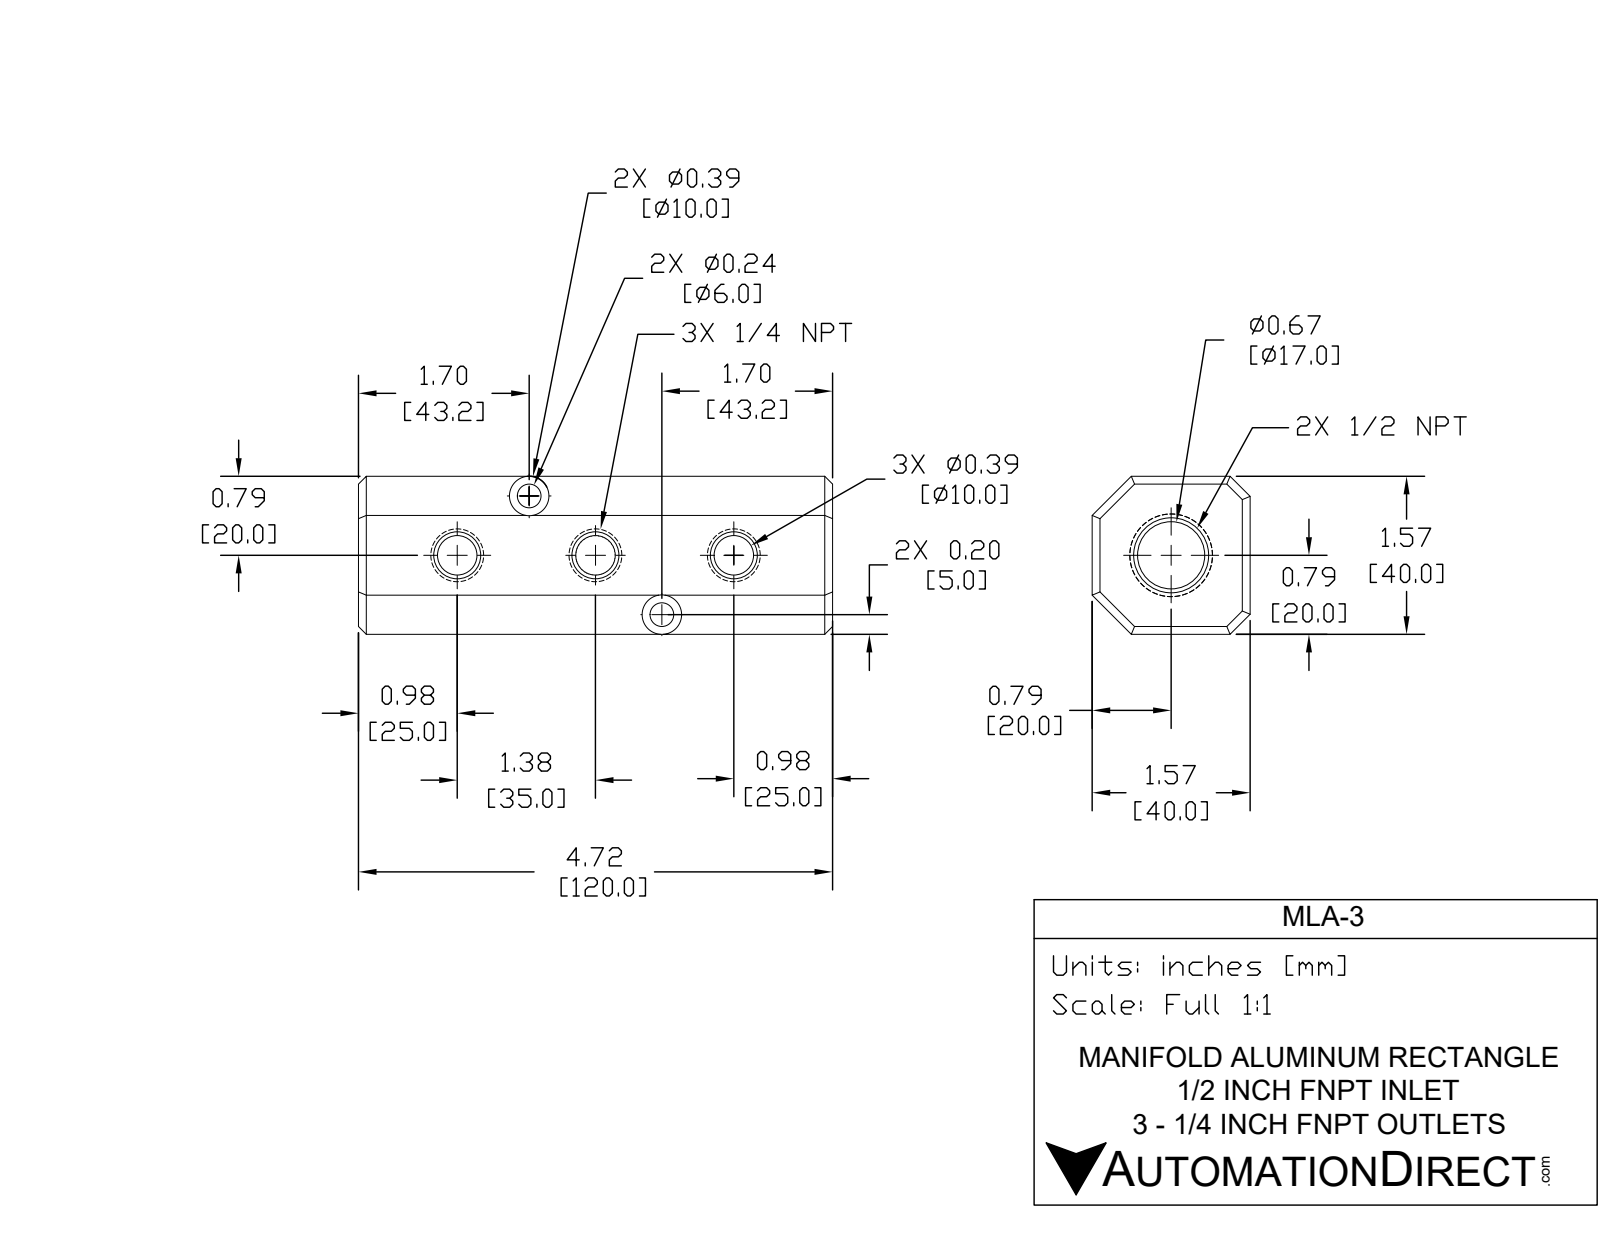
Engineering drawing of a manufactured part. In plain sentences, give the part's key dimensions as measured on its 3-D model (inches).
The part is named "MYA-4". Its 3-D file was written by "SolidWorks 2015 (CONFIG_CONTROL_DESIGN)". It is 1 solid with 74 faces: 30 planar, 34 cylindrical and 10 other. Overall it measures 4.724 by 1.574 by 1.574 inches. Its volume is 8.456 cubic inches and its surface area 44.14 square inches. Round holes: 5 of diameter 0.393, 3 of diameter 0.468, 2 of diameter 0.236, 1 of diameter 0.669, 1 of diameter 0.747. The main face-to-face distances are 1.574, 1.808, 4.724, 4.343, 1.181, 0.393, 4.509. The hole center spacings are 0.887, 0.929, 1.378, 2.123, 0.886, 0.887, 1.377, 1.379.
